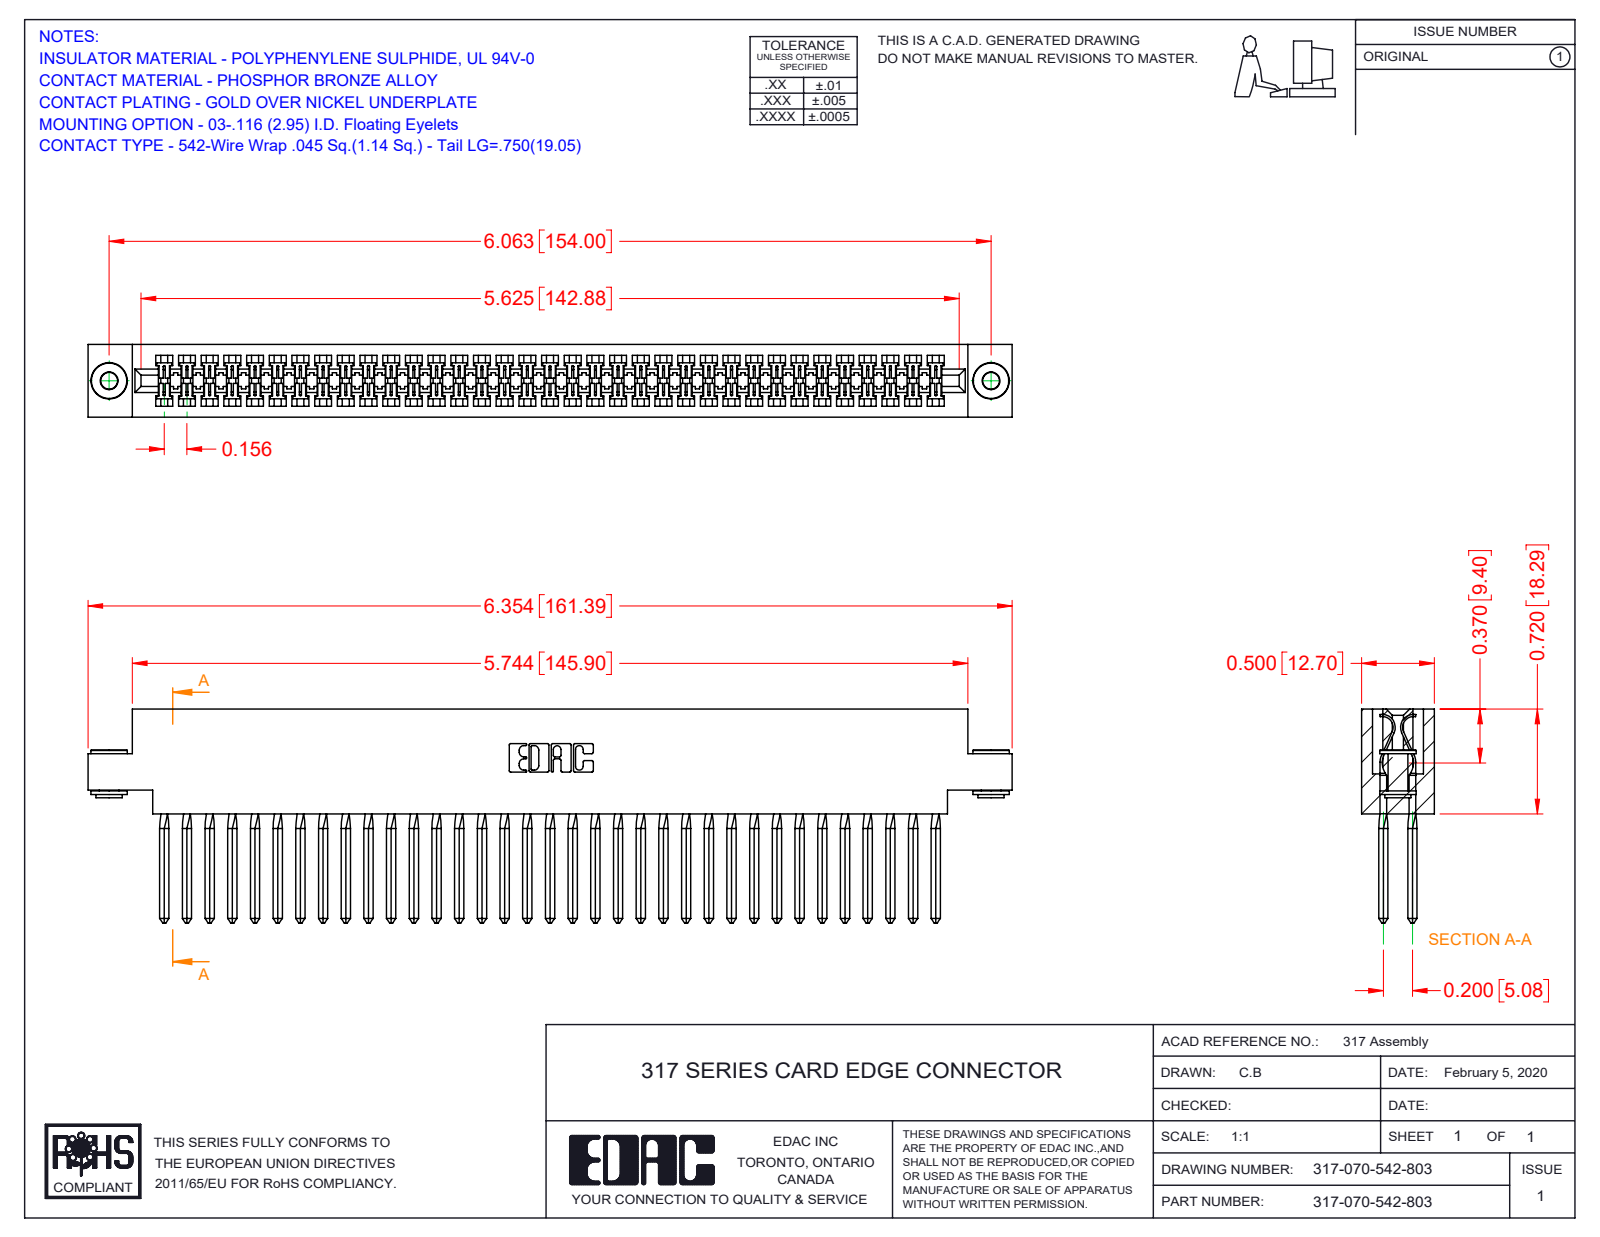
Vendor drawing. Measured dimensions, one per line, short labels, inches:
name: 317-070-542-803; 317-290-003_542; 317 Part_.156 Dia - TH; 345-250-002_345-250-002-102
written by: SolidWorks 2016 (CONFIG_CONTROL_DESIGN)
unit: in
bodies: 73 solids, 4130 faces (3288 planar, 554 cylindrical, 288 other)
size: 6.354 × 1.47 × 0.5
volume: 1.6 in³; area: 56.51 in²
holes: 2× ⌀0.116, 2× ⌀0.156
bosses: 2× ⌀0.25, 2× ⌀0.18, 2× ⌀0.136
rounds: 140× R0.006, 22× R0.01, 6× R0.007, 6× R0.031, 3× R0.026, 2× R0.074, 2× R0.089, 2× R0.1
face distances: 0.5, 0.075, 0.425, 0.35, 0.2, 0.046, 0.128, 0.372, 0.052, 0.297
hole spacings: 6.063
